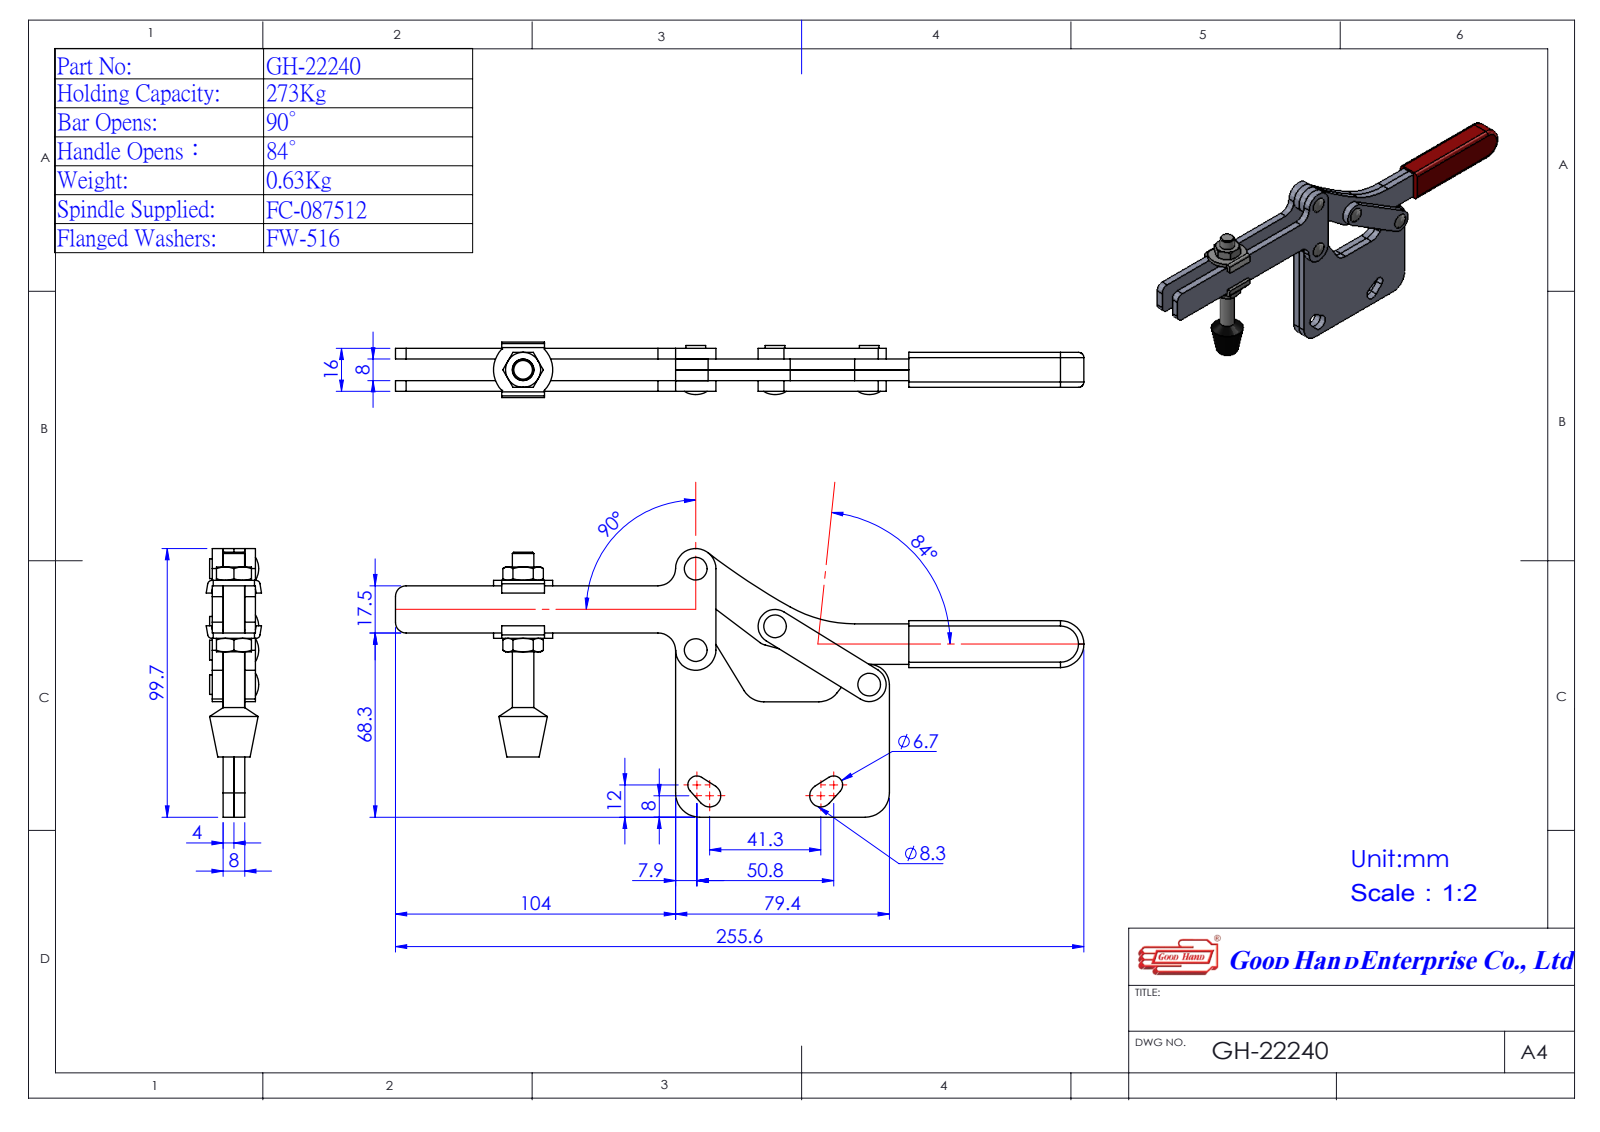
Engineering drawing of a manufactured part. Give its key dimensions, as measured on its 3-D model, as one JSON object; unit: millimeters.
{"part_name": "Group4^GH-22240(簡化)-1; GH-22240(簡化)-1; 12223501-1^GH-22240(簡化)-1; Group2^GH-22240(簡化)-1 (+2 more)", "step_written_by": "SolidWorks 2016 (AUTOMOTIVE_DESIGN)", "units": "millimeters", "bodies": {"solids": 5, "faces": 250, "planar": 111, "cylindrical": 101, "other": 38}, "overall_size": [255.6, 111.22, 20.55], "volume_mm3": 90645, "surface_area_mm2": 43282, "round_holes": [[5, 4]], "round_bosses_or_shafts": [[7.3, 4], [15, 1], [7.93, 1]], "partial_cylinders_radius": [[1.5, 4], [3.35, 2], [4, 2], [4.15, 2], [5, 2], [6.3, 2], [6.5, 2], [7.5, 2]], "face_to_face_distances": [8, 4, 12, 16, 2.5, 1.5, 14.5, 6.5, 10.5, 13], "hole_center_spacings": [30.2, 30.73, 36.39, 41.1, 65.66, 77.44]}
